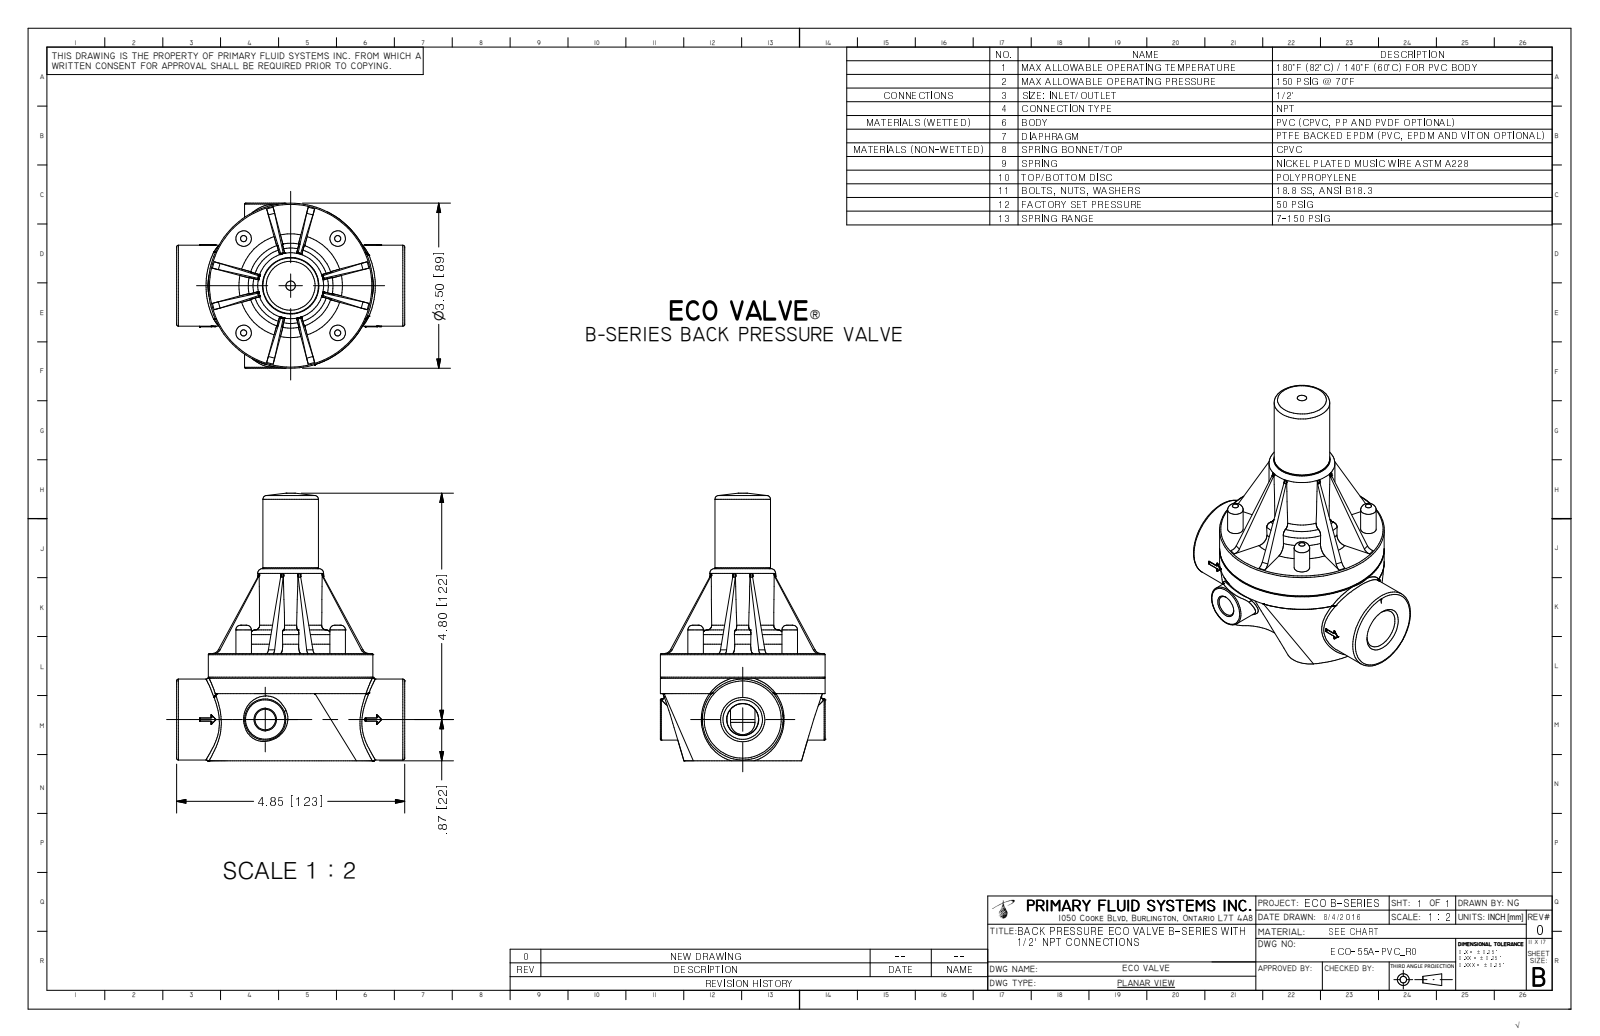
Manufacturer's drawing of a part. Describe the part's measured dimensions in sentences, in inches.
The part is named "ECO-55A-PVC_R0". Its 3-D file was written by "Autodesk Inventor 2009 (AUTOMOTIVE_DESIGN)". It is 1 solid with 340 faces: 139 planar, 84 cylindrical and 117 other. Overall it measures 5.675 by 4.85 by 3.5 inches. Its volume is 27.45 cubic inches and its surface area 106.3 square inches. Round holes: 4 of diameter 0.23, 4 of diameter 0.257, 4 of diameter 0.4, 1 of diameter 0.256, 1 of diameter 0.437. Round bosses or shafts: 4 of diameter 0.33, 3 of diameter 0.256, 1 of diameter 3.5, 1 of diameter 1.8, 1 of diameter 1.716, 1 of diameter 1.4, 1 of diameter 1.18, 1 of diameter 0.875. Partial cylindrical surfaces (rounded edges, fillets, slot ends): 8 of radius 0.1, 8 of radius 0.15, 4 of radius 0.05, 3 of radius 0.128, 1 of radius 0.418, 1 of radius 0.514, 1 of radius 0.669, 1 of radius 0.868. The main face-to-face distances are 2.275, 4.85, 1.75, 0.525, 0.2, 1.55, 2.075, 0.27, 1.6, 3.5. The hole center spacings are 2, 2.828, 2, 2, 2.828, 2.829.
